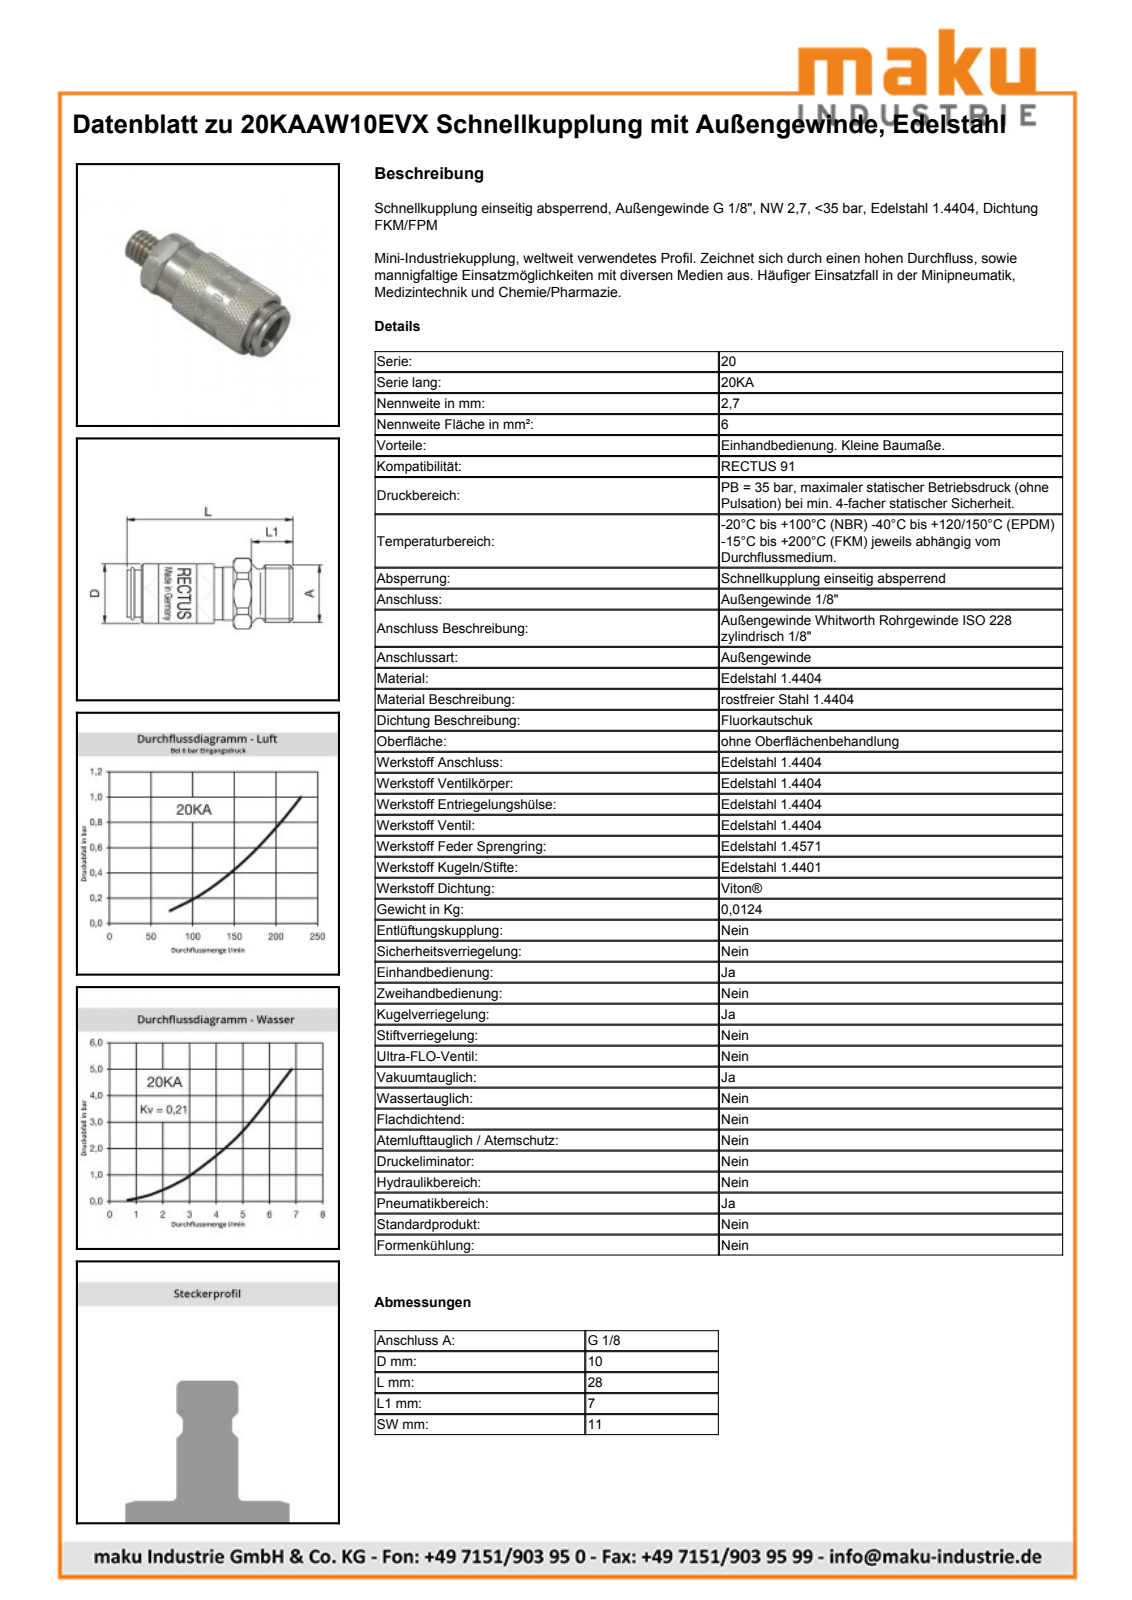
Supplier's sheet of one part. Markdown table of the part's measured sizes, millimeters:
| quantity | value |
| --- | --- |
| part name | D107418 |
| STEP written by | Autodesk Inventor 2013 (AUTOMOTIVE_DESIGN) |
| units | millimeters |
| bodies | 3 solids, 431 faces (158 planar, 66 cylindrical, 207 other) |
| overall size | 28.05 × 11.96 × 11.73 |
| volume | 284 mm³ |
| surface area | 2 019 mm² |
| round holes (diameter × count) | 7.3 × 1, 8.15 × 1, 9.15 × 1, 9.2 × 1 |
| round bosses / shafts (diameter × count) | 10.35 × 1, 10 × 1, 9.73 × 1, 9 × 1, 8.1 × 1, 8 × 1, 7.8 × 1, 7.46 × 1 |
| partial cylindrical surfaces (radius × count) | 4.9 × 1, 5.9 × 1, 6 × 1 |
| main face-to-face distances | 28.05, 18, 10.05, 11, 3.3, 13.35, 5, 2.4, 15.6, 25.65 |
